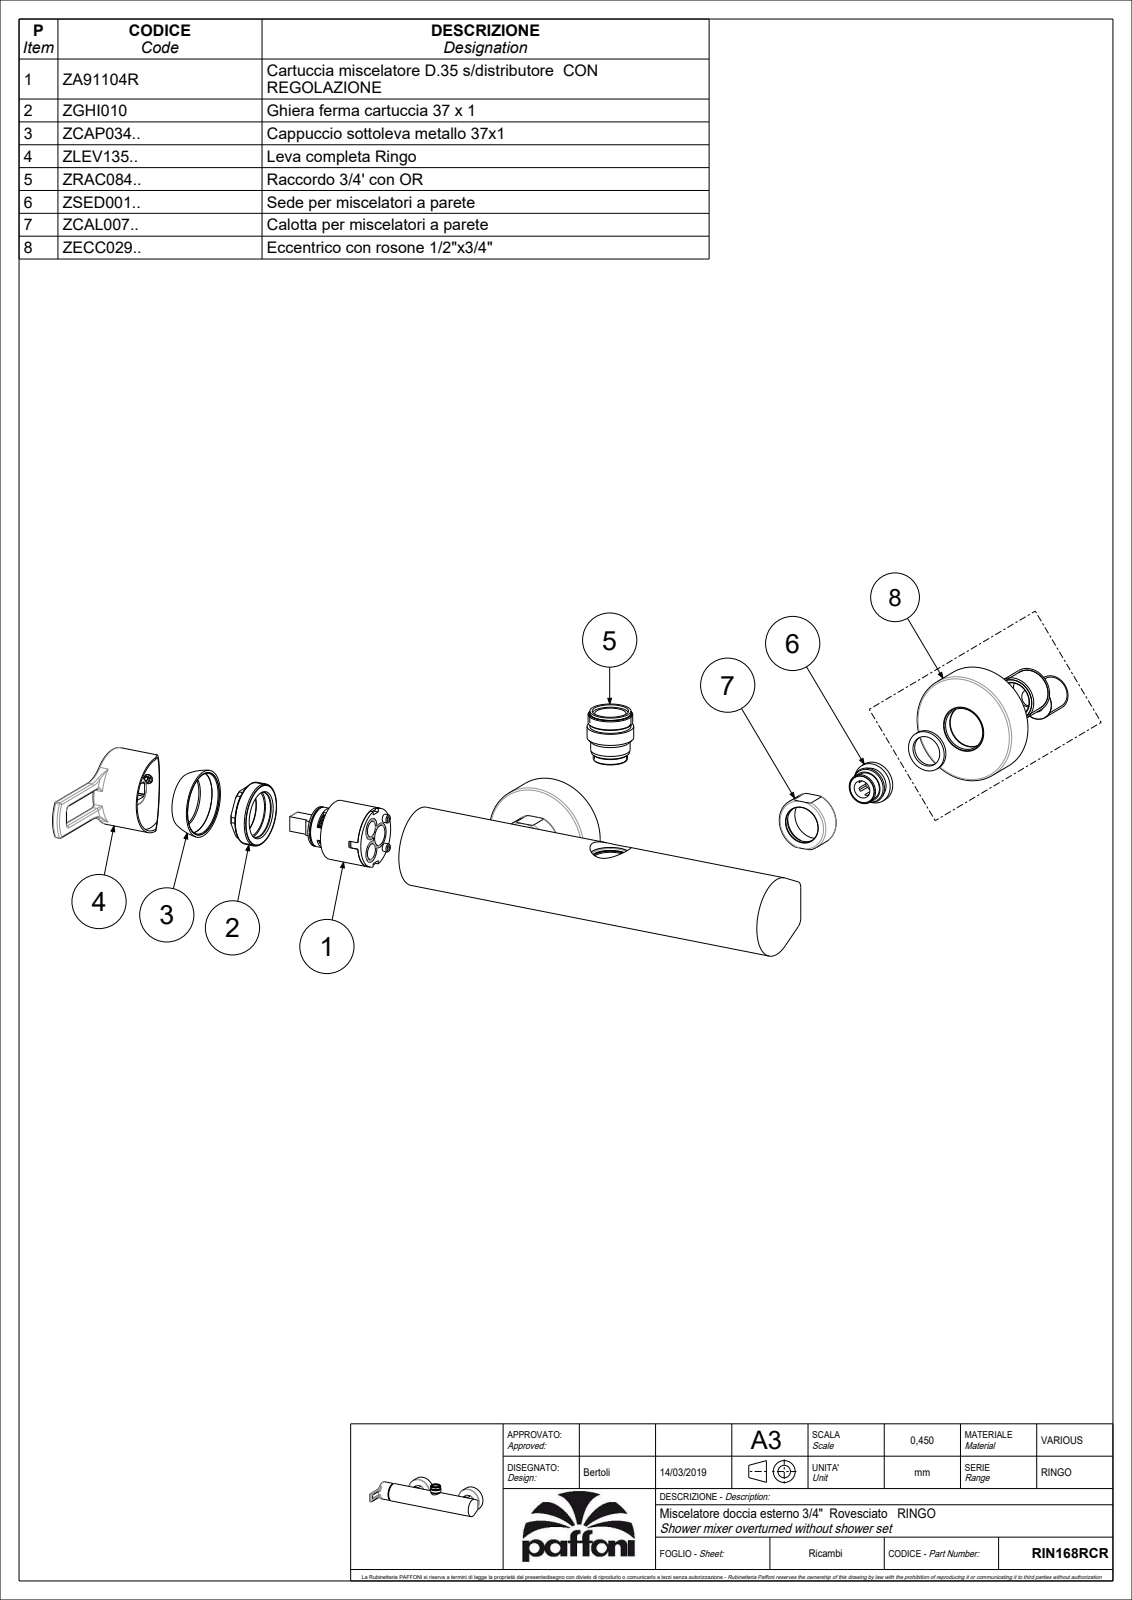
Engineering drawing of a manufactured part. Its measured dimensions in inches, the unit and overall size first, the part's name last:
Units: inches
Overall size (bounding box): 10.748 × 5.234 × 2.921
Round holes (diameter × count): ⌀0.276 ×3, ⌀0.413 ×3, ⌀0.787 ×3, ⌀0.157 ×2, ⌀0.374 ×2, ⌀0.709 ×2, ⌀0.85 ×2, ⌀2.453 ×2, ⌀0.118 ×1, ⌀0.13 ×1, ⌀0.138 ×1, ⌀0.197 ×1
Round bosses / shafts (diameter × count): ⌀2.5 ×2, ⌀1.063 ×2, ⌀1.031 ×2, ⌀0.906 ×2, ⌀0.807 ×2, ⌀0.697 ×2, ⌀1.791 ×1, ⌀1.398 ×1
Partial cylindrical surfaces — rounded edges, fillets, slot ends (radius × count): R0.059 ×44, R0.02 ×34, R0.039 ×14, R0.006 ×11, R0.012 ×4, R0.051 ×4, R0.236 ×4, R0.079 ×2
Main face-to-face distances: 0.146, 0.024, 0.138, 1.173, 1.15, 0.591, 1.035, 0.559, 0.413, 1.012
Hole centre spacings: 0.278, 0.339, 0.449, 5.906, 0.157, 0.236, 0.394, 0.433
Volume: 16.47 in³ · Surface area: 255.4 in²
Bodies: 2 solids, 1559 faces (748 planar, 426 cylindrical, 385 other)
Part name (STEP PRODUCT): RIN168RCR
STEP written by: CREO PARAMETRIC BY PTC INC, 2020044 (CONFIG_CONTROL_DESIGN)
